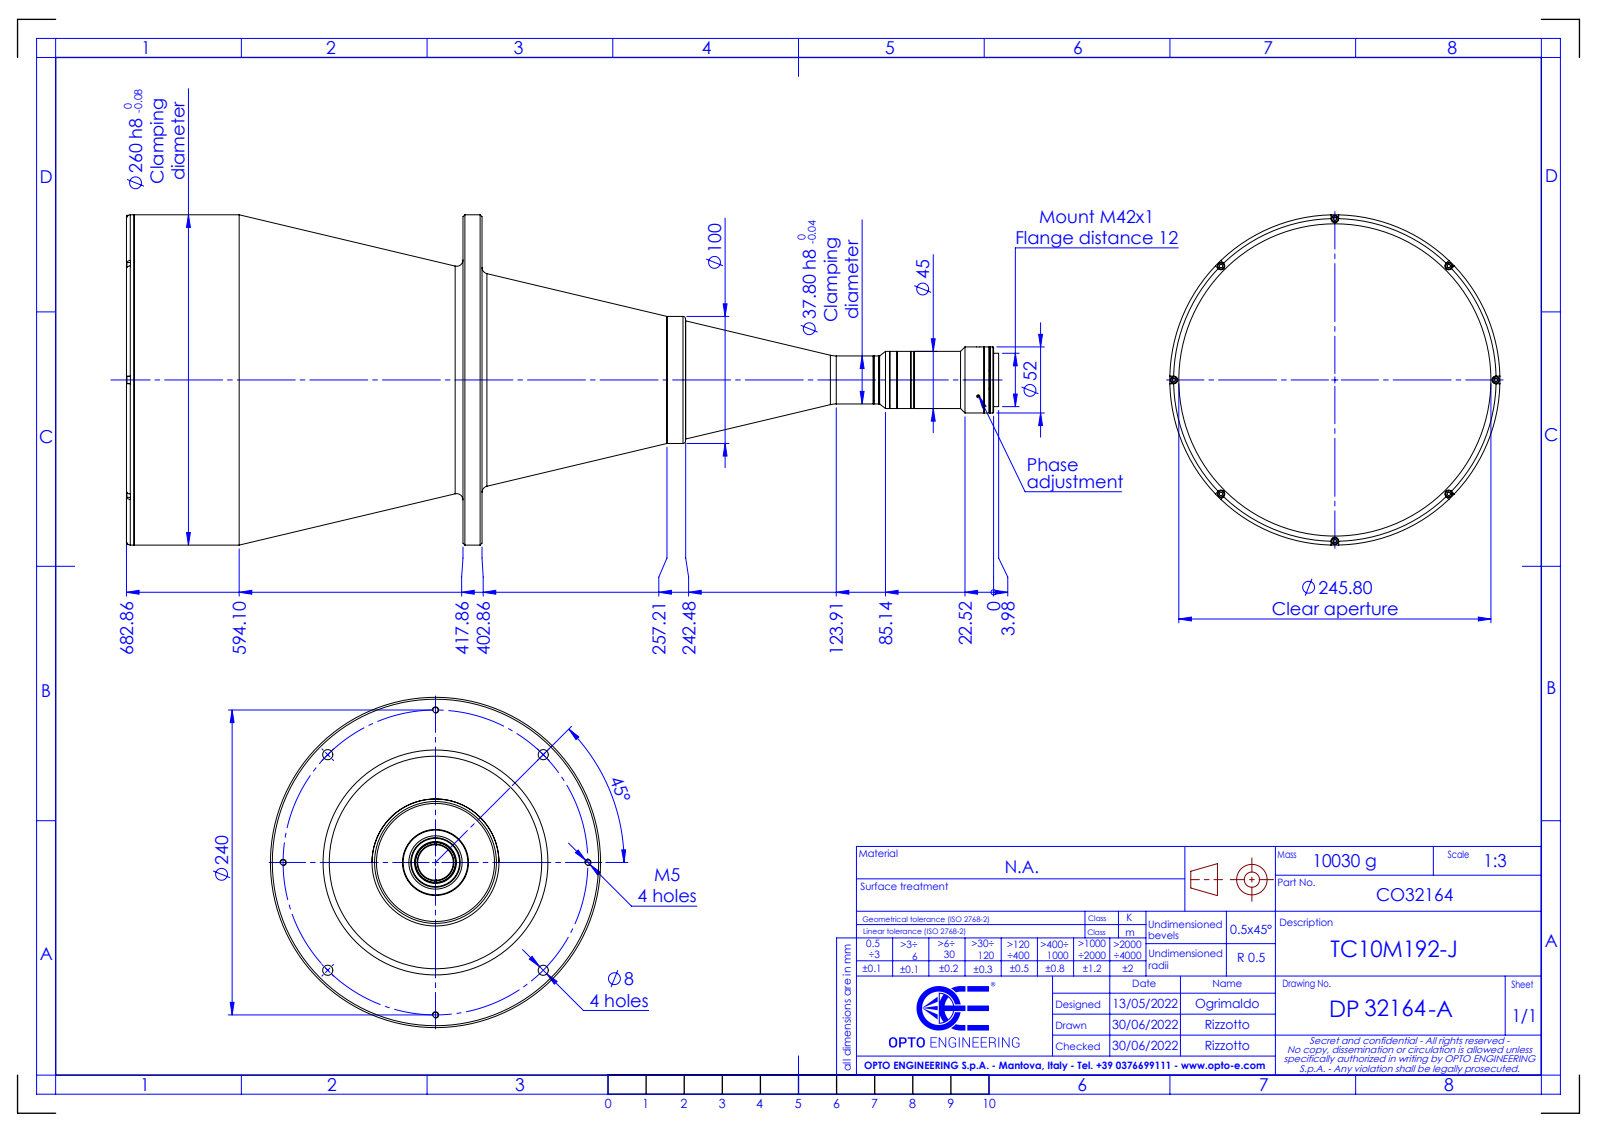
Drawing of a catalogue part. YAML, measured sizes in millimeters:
part_name: "DP32164-A_TC10M192-J"
step_written_by: "SolidWorks 2021 (CONFIG_CONTROL_DESIGN)"
units: millimeters
bodies: {solids: 0, faces: 196, planar: 52, cylindrical: 94, other: 50}
overall_size: [686.84, 260, 260]
round_holes:
  - {diameter: 4.2, count: 4}
  - {diameter: 8, count: 4}
  - {diameter: 2.5, count: 3}
  - {diameter: 38, count: 1}
  - {diameter: 41, count: 1}
  - {diameter: 245.8, count: 1}
  - {diameter: 255, count: 1}
round_bosses_or_shafts:
  - {diameter: 5.5, count: 8}
  - {diameter: 260, count: 1}
  - {diameter: 100, count: 1}
  - {diameter: 93, count: 1}
  - {diameter: 52, count: 1}
  - {diameter: 51.8, count: 1}
  - {diameter: 45, count: 1}
  - {diameter: 42, count: 1}
partial_cylinders:
  - {radius: 3, count: 4}
face_to_face_distances: [15, 265, 280, 18, 247, 262, 680.3, 662.3, 415.3, 400.3]
hole_center_spacings: [91.84, 120, 221.73, 169.7, 169.71, 239.99, 240]
